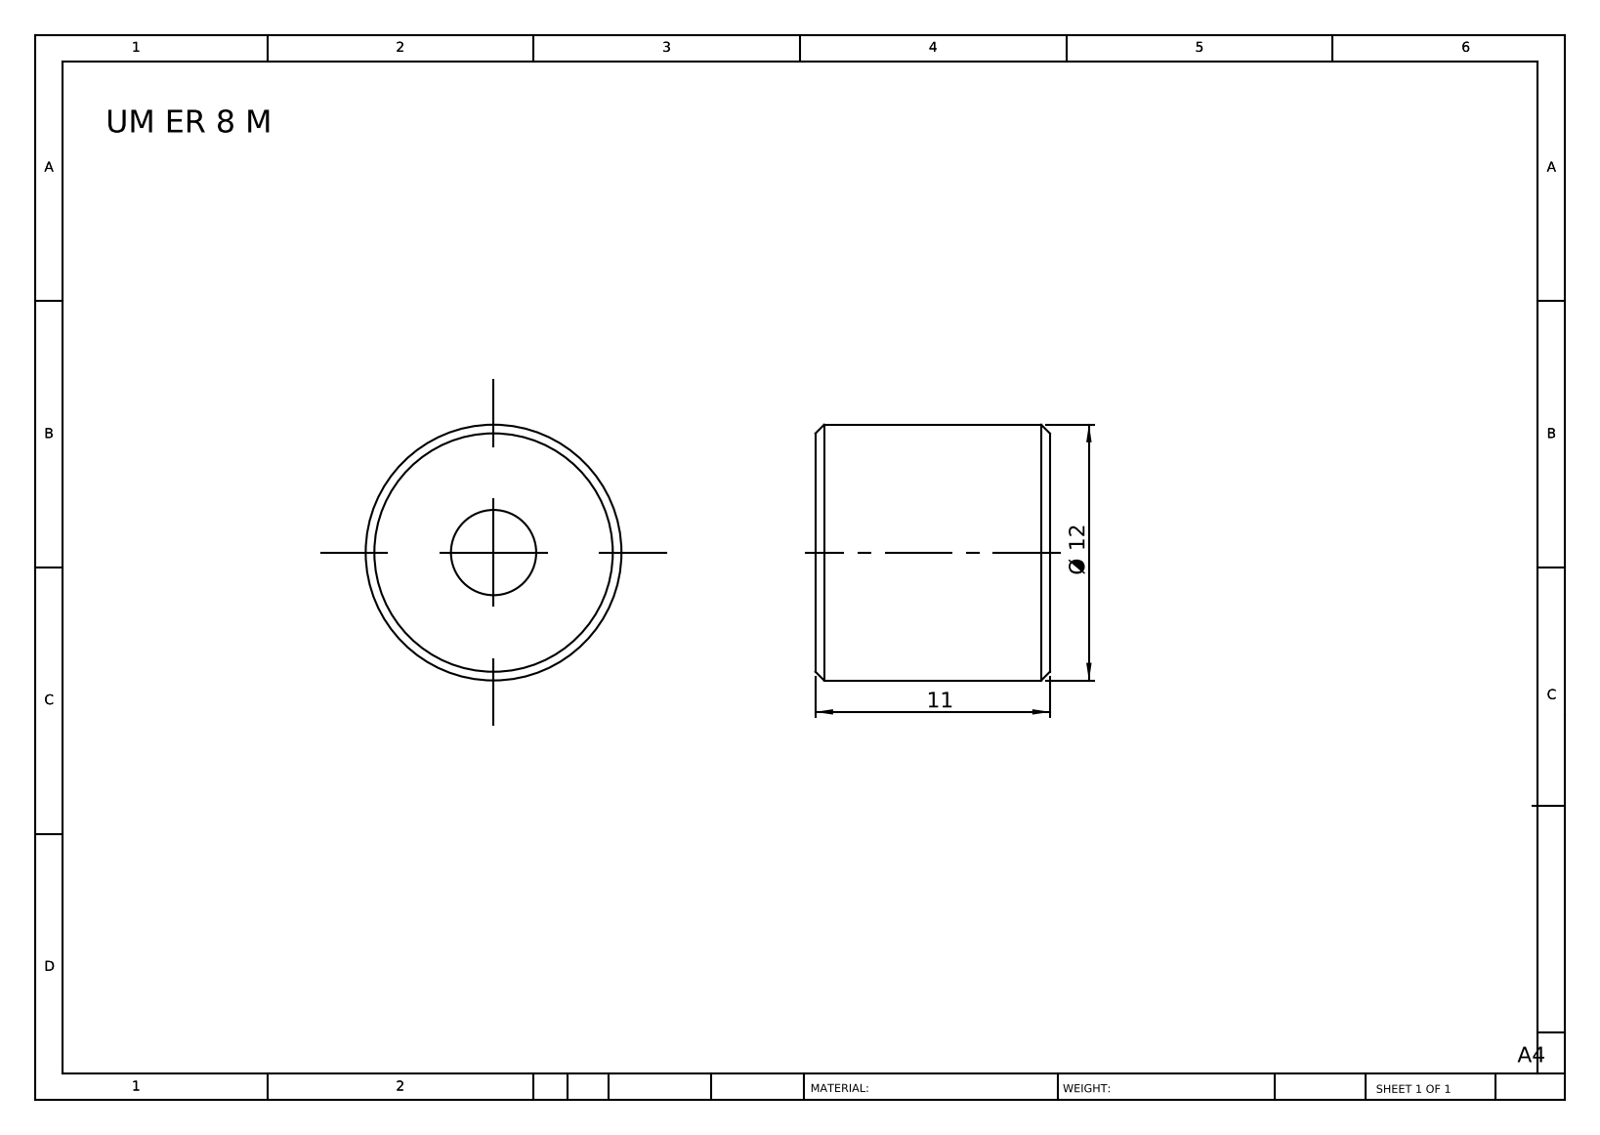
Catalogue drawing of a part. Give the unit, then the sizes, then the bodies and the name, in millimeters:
Units: millimetres
Overall size (bounding box): 12 × 12 × 11
Round holes (diameter × count): ⌀4 ×1
Round bosses / shafts (diameter × count): ⌀12 ×1
Main face-to-face distances: 11
Volume: 1 100 mm³ · Surface area: 736 mm²
Bodies: 1 solid, 10 faces (2 planar, 4 cylindrical, 4 other)
Part name (STEP PRODUCT): UM ER 8 M
STEP written by: SolidWorks 2014 (CONFIG_CONTROL_DESIGN)
